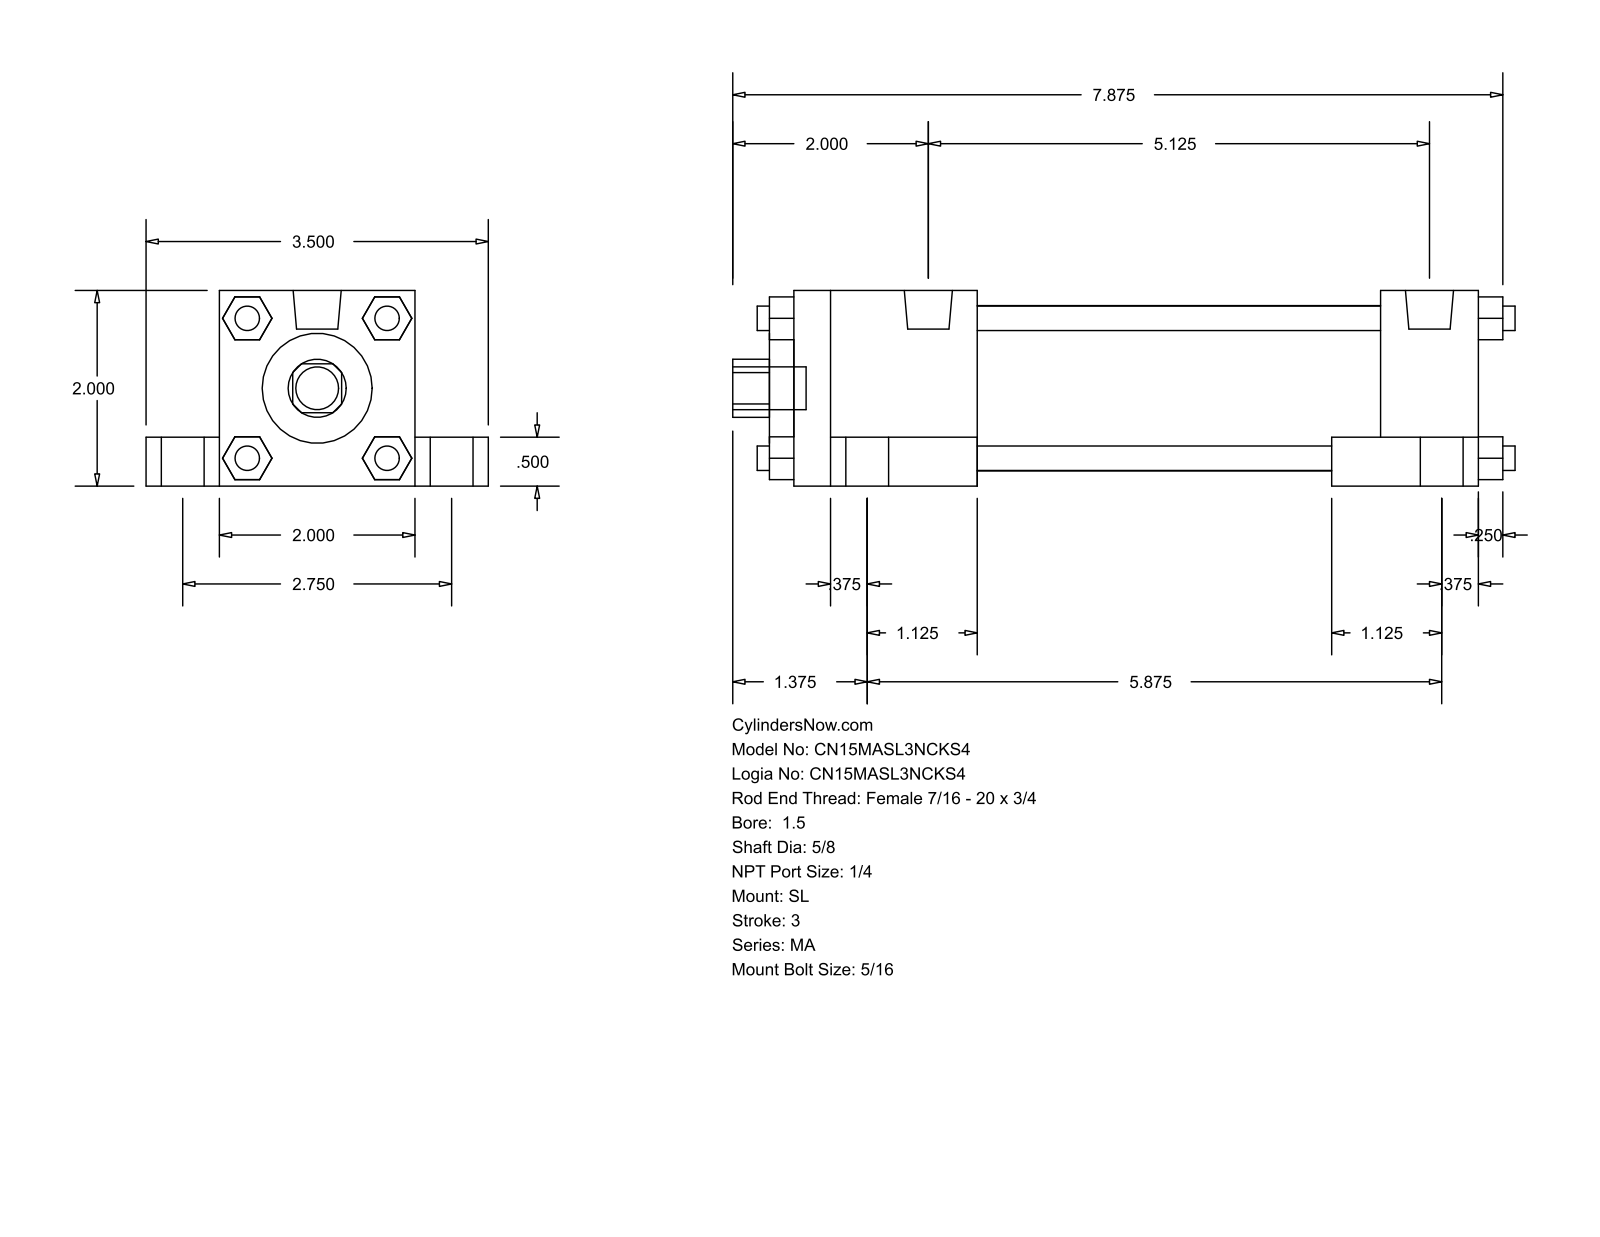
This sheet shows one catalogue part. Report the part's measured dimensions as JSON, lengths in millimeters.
{"part_name": "MA_SL__0150_0.625", "step_written_by": "GSSL Pune (CONFIG_CONTROL_DESIGN)", "units": "millimeters", "bodies": {"solids": 0, "faces": 148, "planar": 112, "cylindrical": 36, "other": 0}, "overall_size": [203.2, 88.9, 50.8], "round_holes": [[15.88, 1], [28.57, 1], [42.93, 1]], "round_bosses_or_shafts": [[11.11, 5], [17.46, 4], [7.94, 4], [6.35, 4], [12.49, 2]], "partial_cylinders_radius": [[7.54, 1]], "face_to_face_distances": [50.8, 19.05, 38.1, 12.7, 177.8, 69.85, 9.52, 6.35, 184.15, 25.4]}
